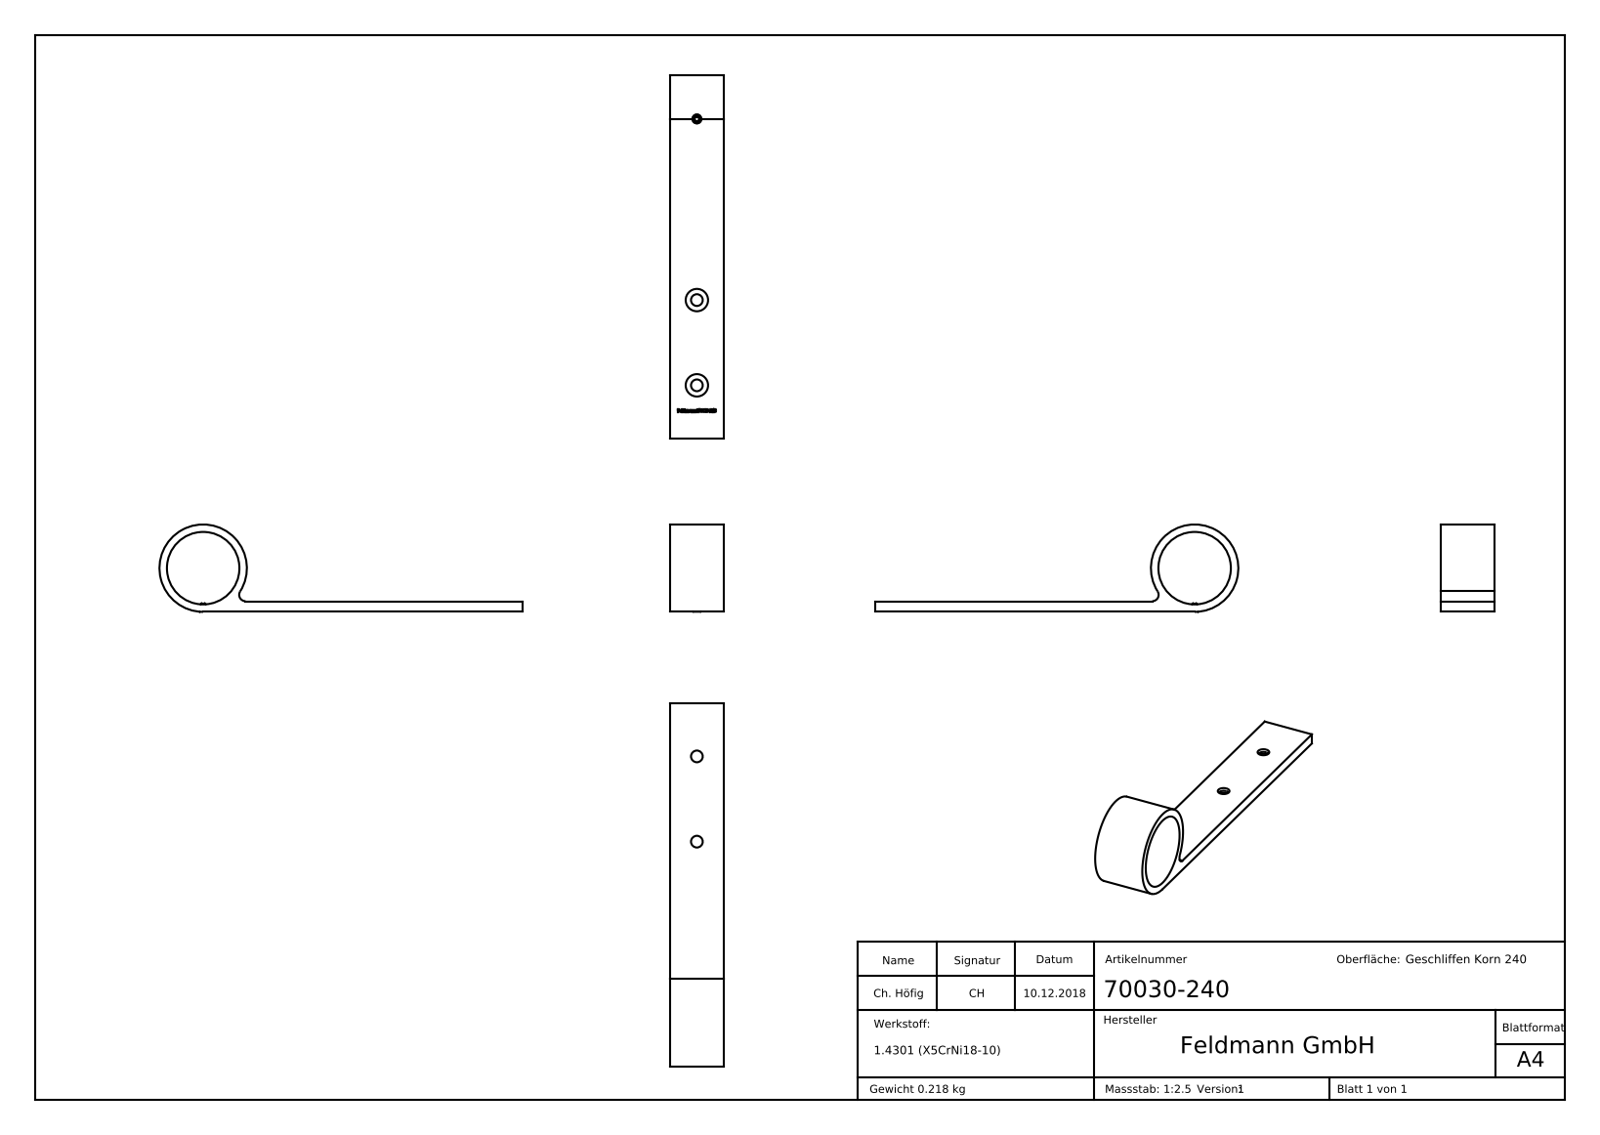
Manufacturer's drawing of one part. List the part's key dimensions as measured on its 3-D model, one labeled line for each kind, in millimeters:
Part name (STEP PRODUCT): 7003X-XXX Teil1_70030-240 Teil1; 70030-240; DIN913 M4x4_DIN913 M4x4
STEP written by: SolidWorks 2015 (CONFIG_CONTROL_DESIGN)
Units: millimetres
Bodies: 2 solids, 256 faces (125 planar, 19 cylindrical, 112 other)
Overall size (bounding box): 170.5 × 41 × 25
Volume: 27 596 mm³ · Surface area: 15 088 mm²
Round holes (diameter × count): ⌀5.5 ×2, ⌀10.5 ×2, ⌀4.2 ×1, ⌀34 ×1
Round bosses / shafts (diameter × count): ⌀41 ×1, ⌀4 ×1
Partial cylindrical surfaces — rounded edges, fillets, slot ends (radius × count): R3 ×1
Main face-to-face distances: 5, 25, 2, 4.9, 1.9, 3, 149, 151, 1, 4
Hole centre spacings: 40, 85, 125
